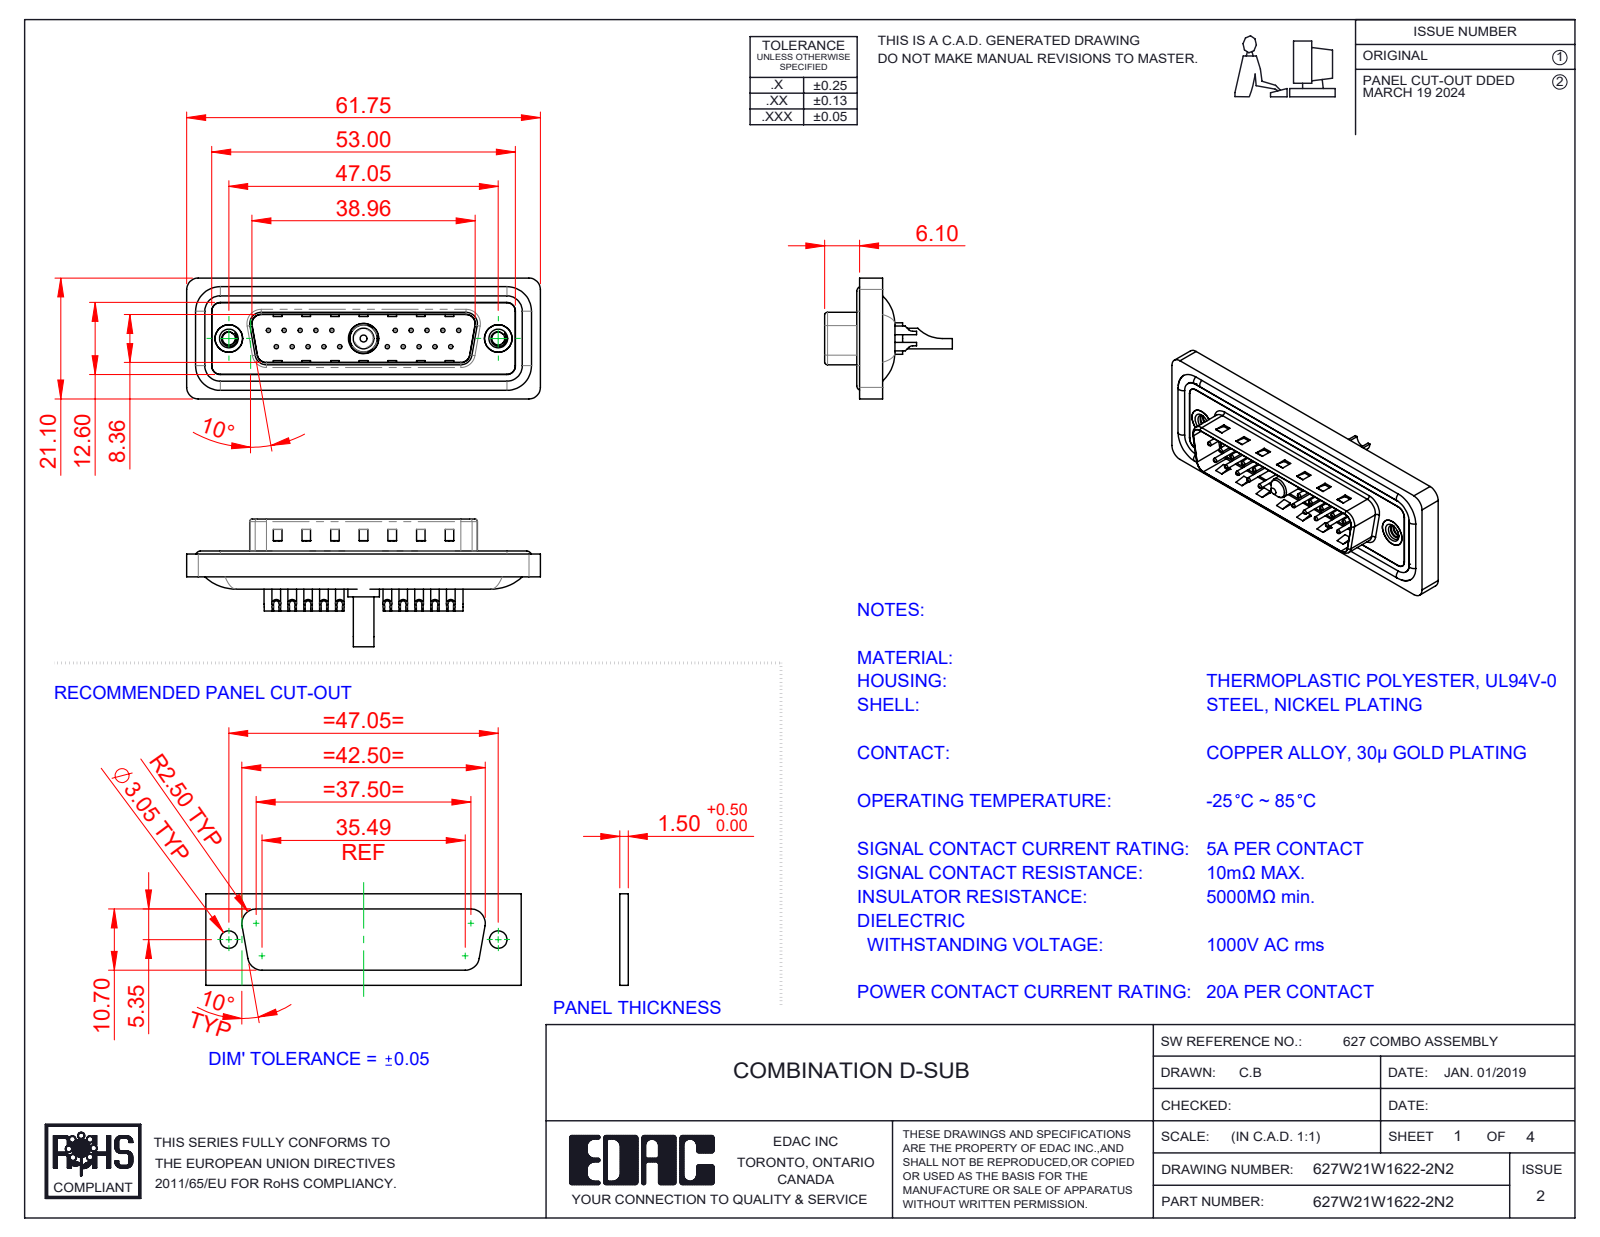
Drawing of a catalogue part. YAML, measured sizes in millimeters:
part_name: "Power Pin_20A SC; 627Combo Shell Front_25 Contacts; 627Combo Waterproof Housing_25 Contacts; 627W21W1622-2N2 (+5 more)"
step_written_by: "SolidWorks 2023 (CONFIG_CONTROL_DESIGN)"
units: millimeters
bodies: {solids: 29, faces: 1269, planar: 402, cylindrical: 530, other: 337}
overall_size: [61.75, 22.3, 21.1]
volume: 7241
surface_area: 12195
round_holes:
  - {diameter: 0.75, count: 20}
  - {diameter: 1, count: 20}
  - {diameter: 1.6, count: 20}
  - {diameter: 2, count: 20}
  - {diameter: 2.26, count: 2}
  - {diameter: 4, count: 2}
  - {diameter: 4.8, count: 2}
  - {diameter: 5, count: 2}
  - {diameter: 2.7, count: 1}
  - {diameter: 4.85, count: 1}
  - {diameter: 5.3, count: 1}
round_bosses_or_shafts:
  - {diameter: 1.5, count: 20}
  - {diameter: 1.6, count: 4}
  - {diameter: 4.9, count: 2}
  - {diameter: 5.5, count: 1}
  - {diameter: 5.2, count: 1}
  - {diameter: 4.75, count: 1}
  - {diameter: 3.75, count: 1}
  - {diameter: 3.6, count: 1}
partial_cylinders:
  - {radius: 1.5, count: 22}
  - {radius: 2, count: 18}
  - {radius: 0.5, count: 8}
  - {radius: 1.6, count: 8}
  - {radius: 1, count: 6}
  - {radius: 0.25, count: 4}
  - {radius: 0.6, count: 4}
  - {radius: 0.65, count: 4}
face_to_face_distances: [0.4, 1.5, 1.1, 1.6, 0.5, 3.1, 2.9, 4.1, 0.82, 9.58]
hole_center_spacings: [3.16, 2.77, 5.54, 8.31, 5.04, 19.39, 20.97, 22.16]
